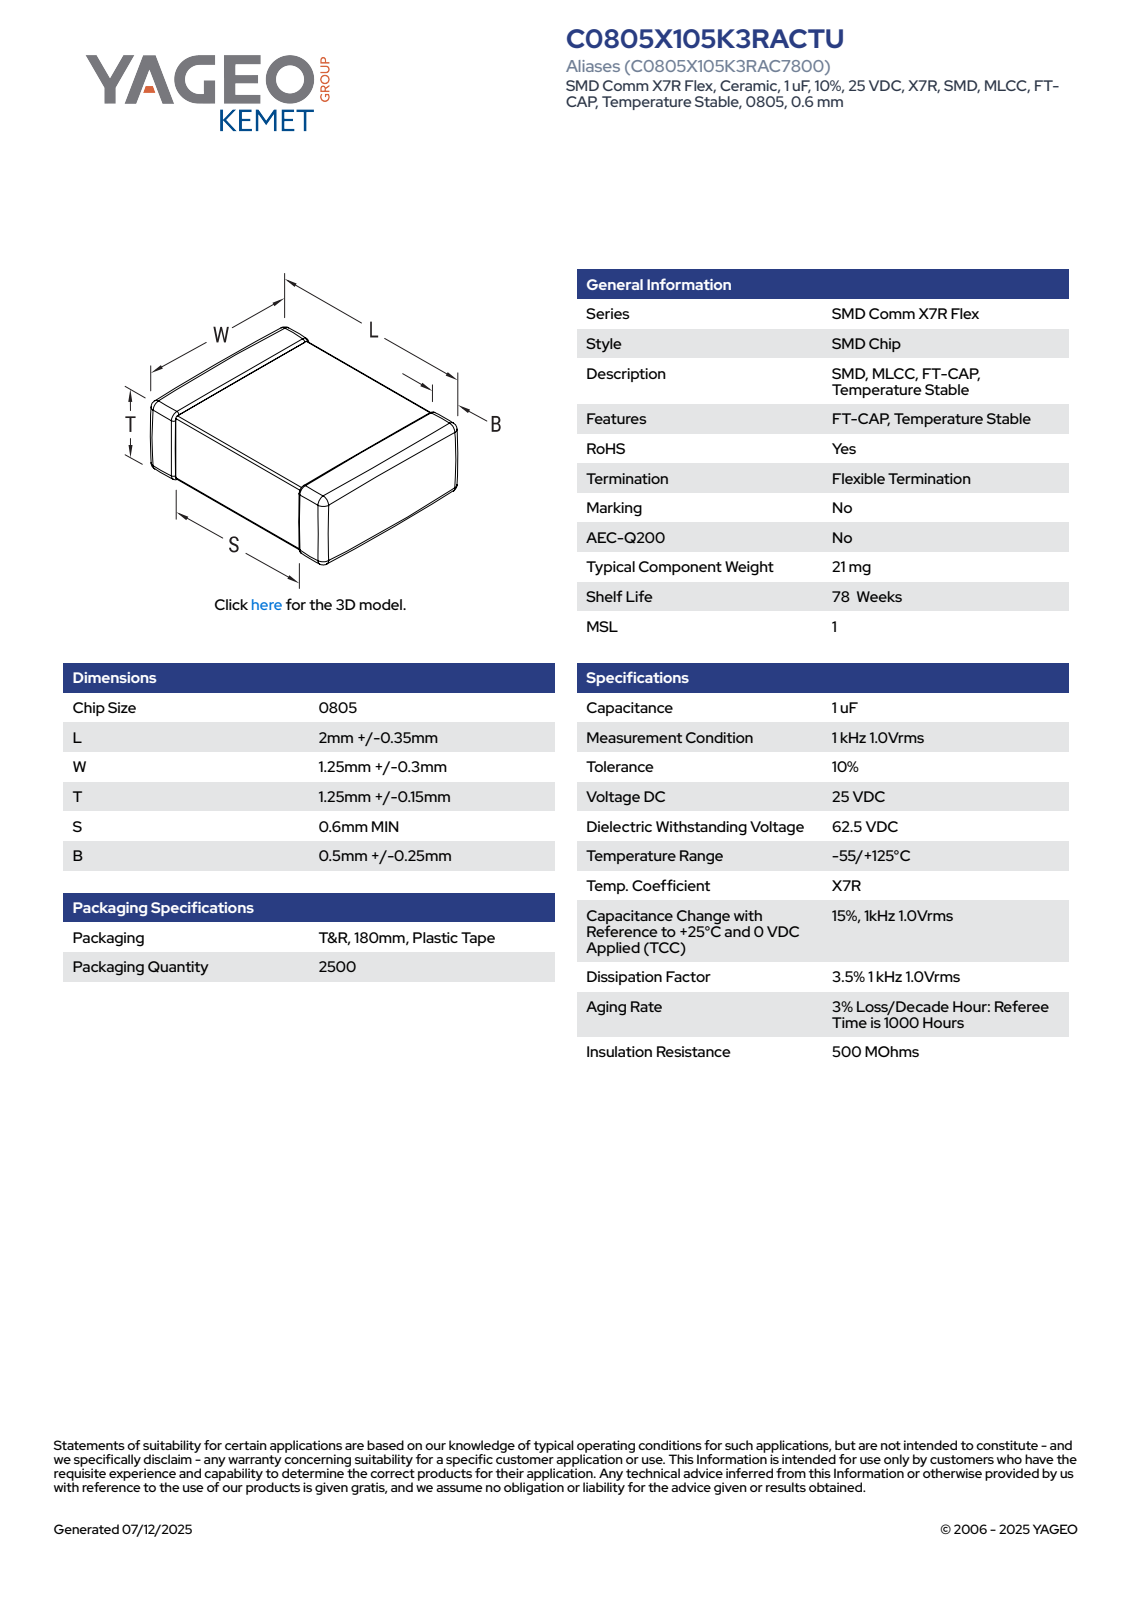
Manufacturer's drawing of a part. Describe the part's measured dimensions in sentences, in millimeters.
The part is named "CCS_CCSTD_0805_L2.35W1.55T1.4B0.5". Its 3-D file was written by "SolidWorks 2021 (AUTOMOTIVE_DESIGN)". It is 4 solids with 125 faces: 71 planar, 38 cylindrical and 16 other. Overall it measures 2.35 by 1.55 by 1.4 millimeters. Its volume is 5 cubic millimeters and its surface area 18 square millimeters. The main face-to-face distances are 1.37, 1.52, 1.4, 2.35, 1.55, 1.34, 1.49, 1.04, 1.31, 1.08.
